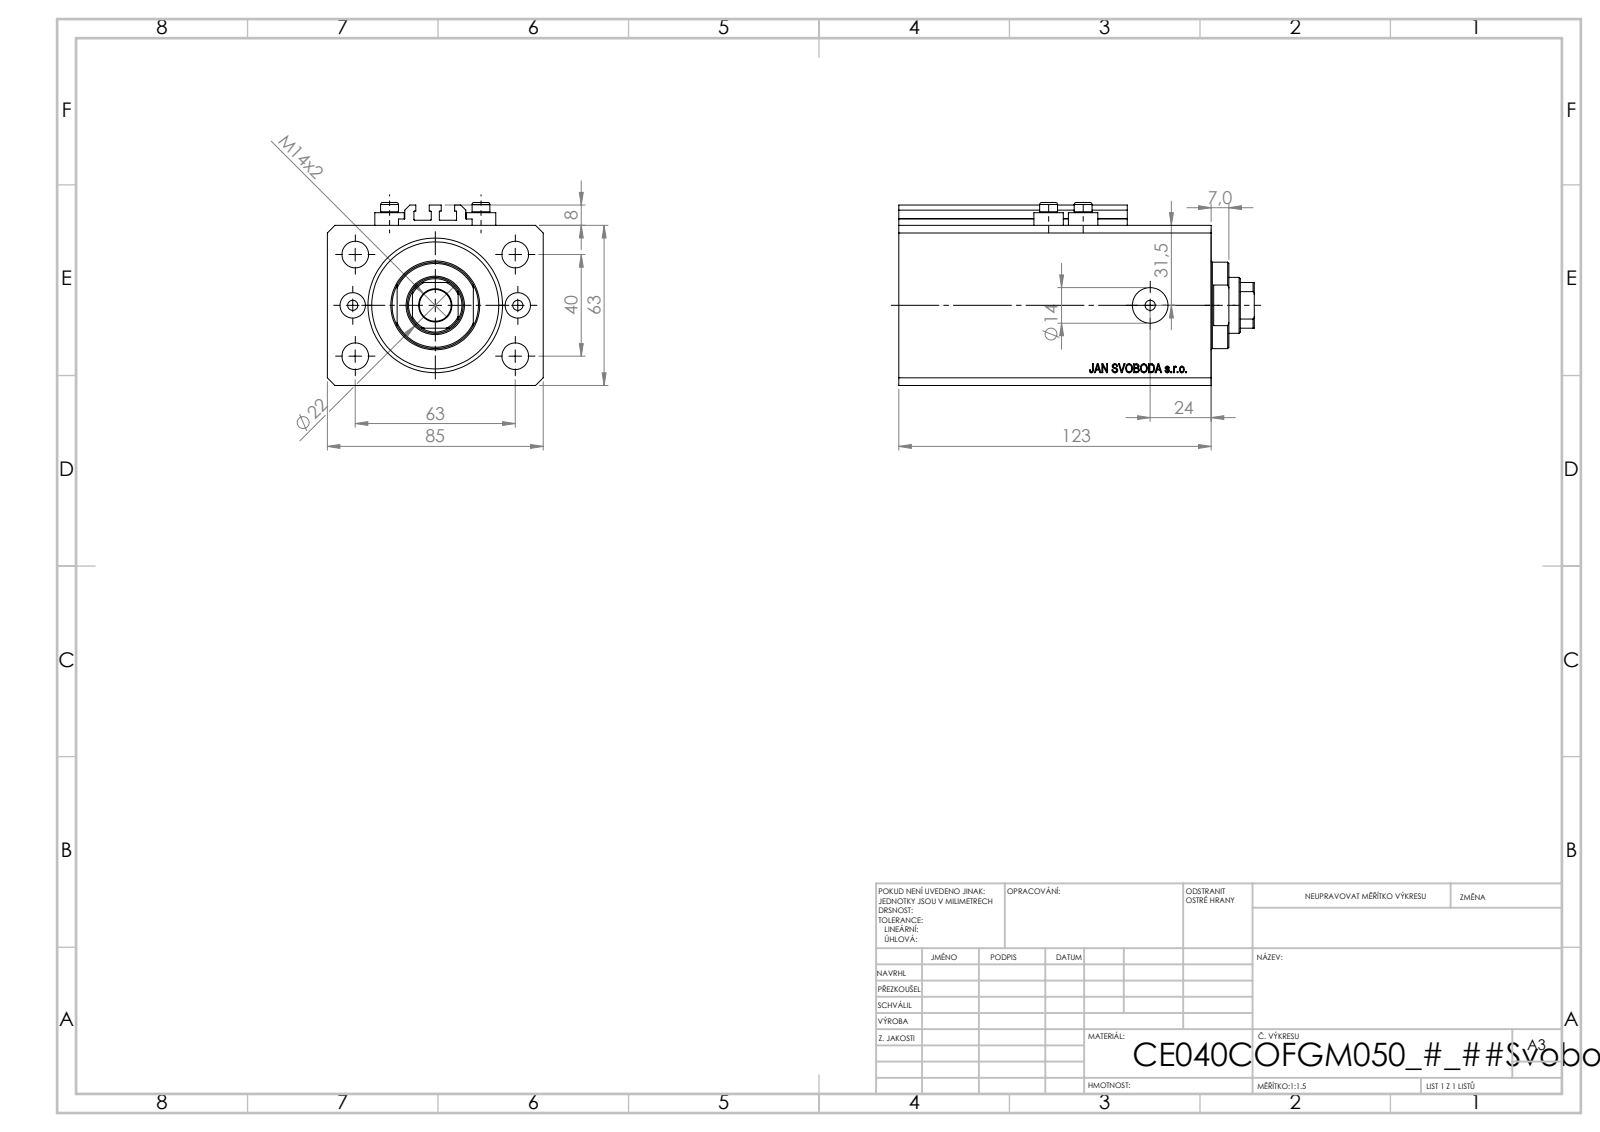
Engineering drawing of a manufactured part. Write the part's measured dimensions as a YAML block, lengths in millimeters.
part_name: "V250CE_C_VCP; V250CE_C_Body; V250CE_VC_C; ALLEN BOLT V250CE"
step_written_by: "SolidWorks 2019 (CONFIG_CONTROL_DESIGN)"
units: millimeters
bodies: {solids: 8, faces: 1034, planar: 504, cylindrical: 86, other: 444}
overall_size: [140, 85, 72]
volume: 587344
surface_area: 113688
round_holes:
  - {diameter: 4, count: 8}
  - {diameter: 10.5, count: 4}
  - {diameter: 10, count: 2}
  - {diameter: 14, count: 2}
  - {diameter: 12.5, count: 1}
  - {diameter: 22, count: 1}
  - {diameter: 40, count: 1}
  - {diameter: 53, count: 1}
round_bosses_or_shafts:
  - {diameter: 11.6, count: 4}
  - {diameter: 7, count: 4}
  - {diameter: 34, count: 1}
partial_cylinders:
  - {radius: 0.2, count: 10}
  - {radius: 10.5, count: 1}
face_to_face_distances: [63, 85, 123, 17, 106, 11.4, 94.6, 111.6, 2.5, 10]
hole_center_spacings: [20.02, 37.31, 67.05, 13.6, 32.5, 36, 38.48, 40]
